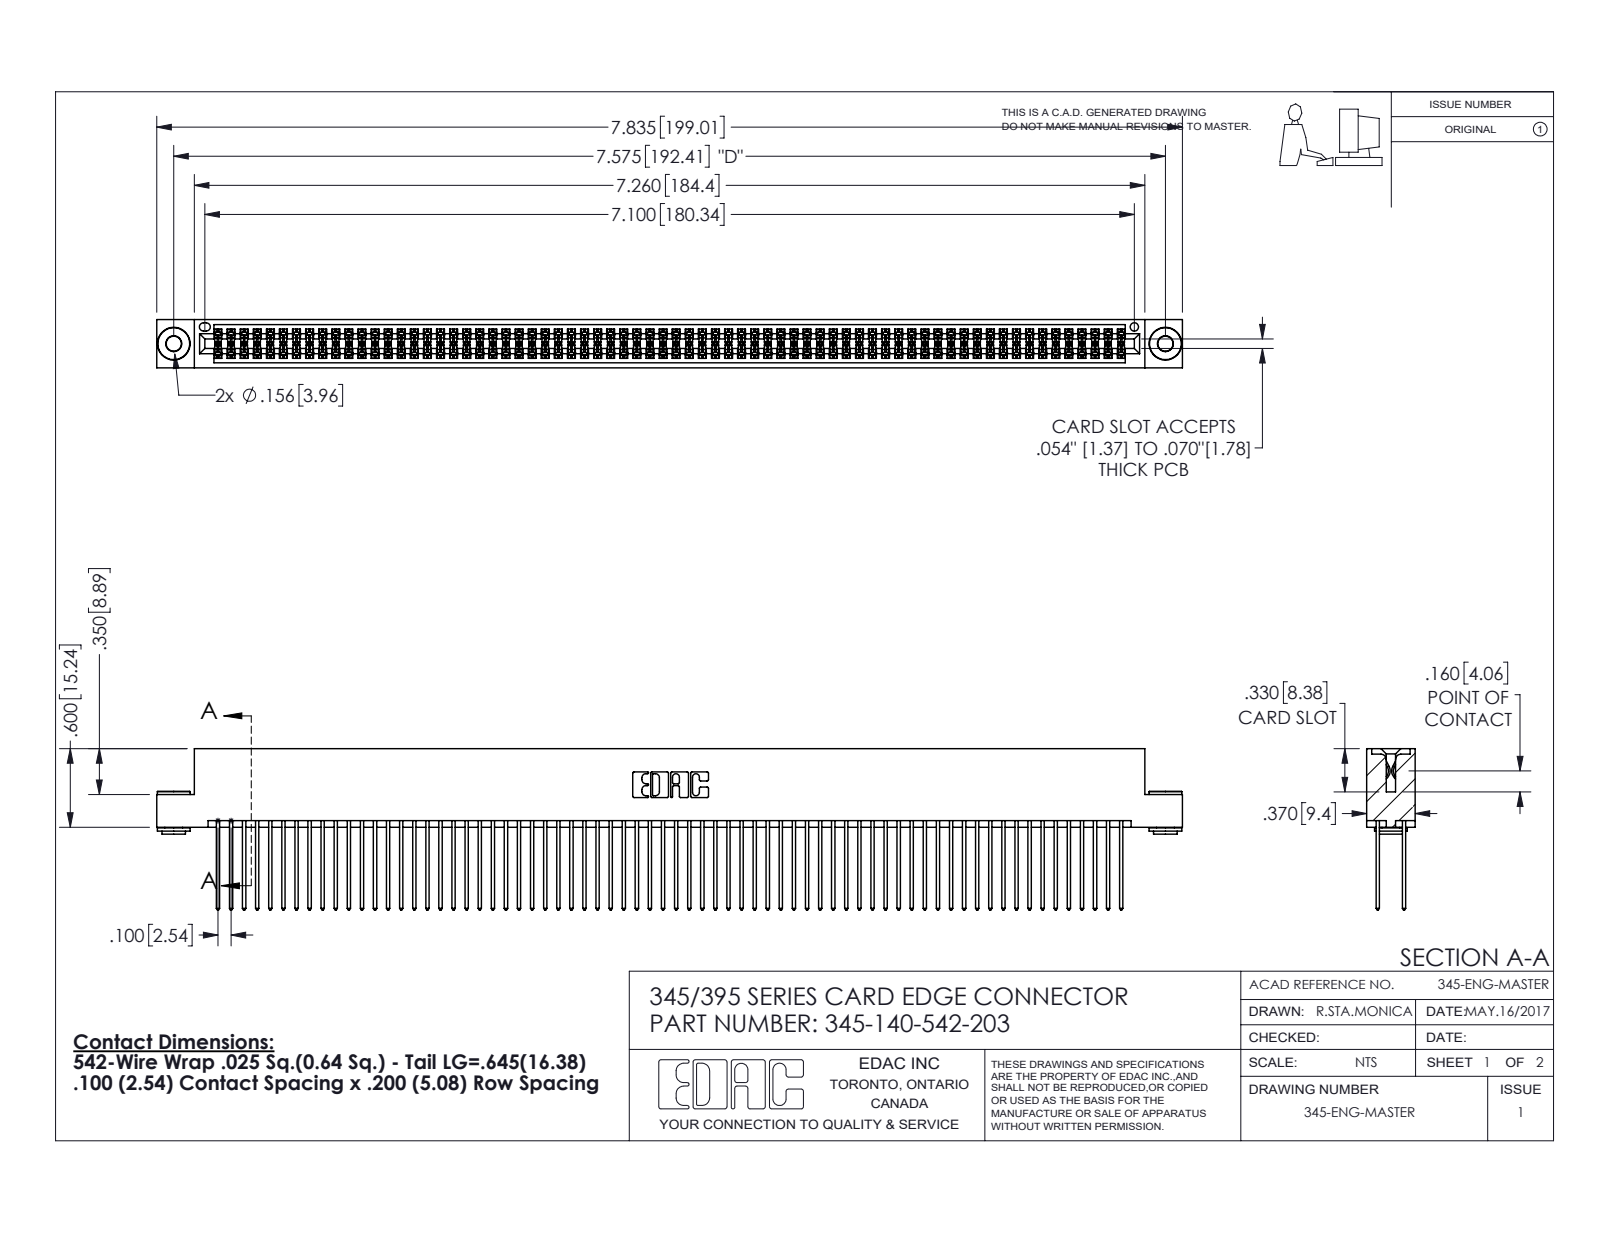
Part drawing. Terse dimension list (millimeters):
name: 345-292-001_345-293-142; 345-140-542-203; 345-250-002_345-250-002-102; 345 Part_Flush Mounting Lugs - 0.156 Dia-TH
written by: SolidWorks 2016 (CONFIG_CONTROL_DESIGN)
unit: mm
bodies: 143 solids, 7164 faces (4710 planar, 2446 cylindrical, 8 other)
size: 199 × 31.3 × 9.4
volume: 20 270 mm³; area: 33 750 mm²
holes: 2× ⌀2.9, 2× ⌀4, 1× ⌀1.6
bosses: 2× ⌀6.4, 2× ⌀4.6, 2× ⌀3.5
rounds: 210× R0.2, 140× R0.3, 22× R0.3, 6× R0.2, 6× R0.8, 3× R0.7, 2× R0.4, 2× R0.5
face distances: 1.8, 7.6, 5.1, 0.6, 2.5, 6.9, 5.7, 9.4, 4.4, 3.8
hole spacings: 6.9, 186.4, 192.4
